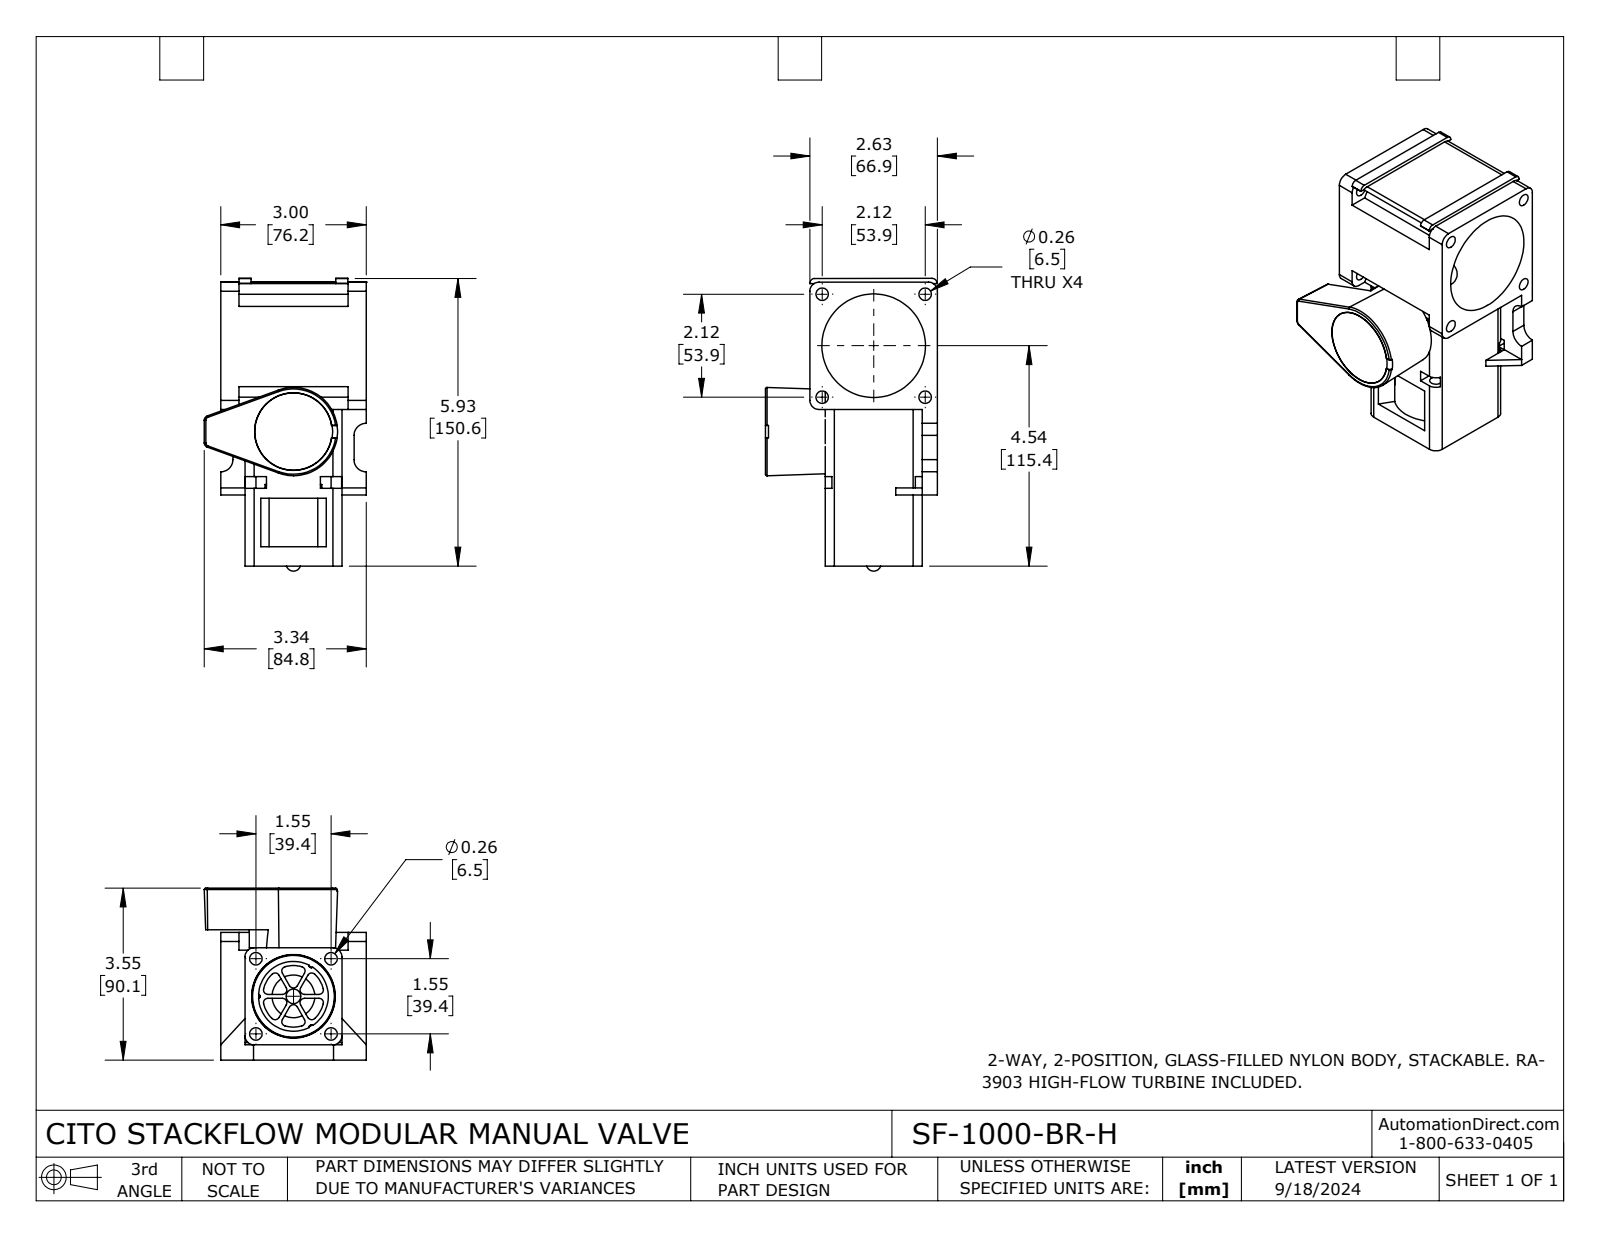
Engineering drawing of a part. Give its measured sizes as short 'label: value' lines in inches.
name: SF-1000-BR-H
written by: SolidWorks 2023 (CONFIG_CONTROL_DESIGN)
unit: in
bodies: 5 solids, 410 faces (173 planar, 205 cylindrical, 32 other)
size: 6.031 × 3.547 × 3.338
volume: 19.15 in³; area: 174 in²
holes: 4× ⌀0.256, 4× ⌀0.257, 1× ⌀0.124, 1× ⌀0.52, 1× ⌀0.88, 1× ⌀1.284, 1× ⌀1.477, 1× ⌀1.484, 1× ⌀1.595, 1× ⌀1.723, 1× ⌀2.136
bosses: 1× ⌀1.6, 1× ⌀1.45, 1× ⌀0.125
rounds: 18× R0.092, 6× R0.046, 4× R0.25, 3× R0.03, 3× R0.187, 2× R0.01, 2× R0.02, 2× R0.1
face distances: 2, 0.316, 2.316, 2.5, 0.5, 2.632, 0.915, 3.231, 3.547, 3
hole spacings: 1.502, 2.124, 1.096, 1.096, 1.55, 1.55, 2.192, 3.003
